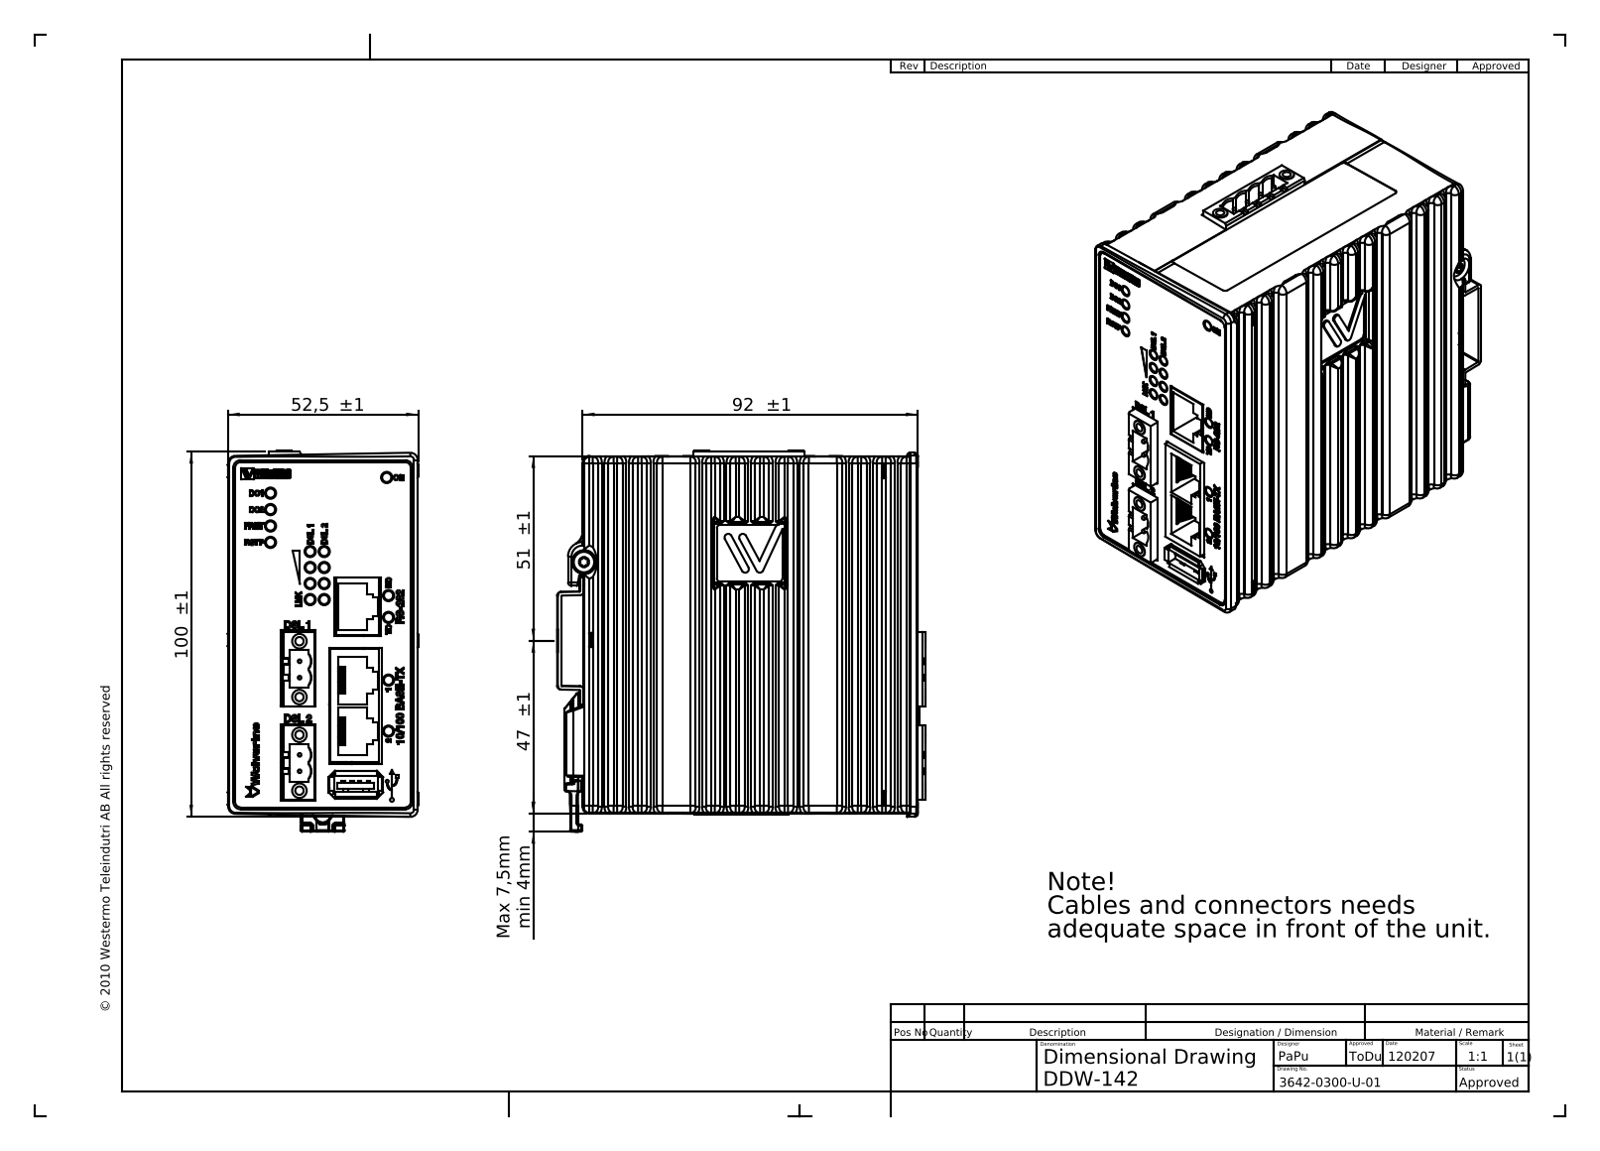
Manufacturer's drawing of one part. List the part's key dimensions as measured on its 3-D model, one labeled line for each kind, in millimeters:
Part name (STEP PRODUCT): 3642-0300; Pan Head Cross Recess Screw_ISO_ISO 7045 - M3 x 6 - Z --- 6N; MRT-TT-M2.5x6H-steel-fzb-Bufab_MRT-TT-M2.5x6H-steel-fzb-Bufab; 9003-0134_assy.encl.DIN_Lock_Lynx_cc (+8 more)
STEP written by: SolidWorks 2011 (CONFIG_CONTROL_DESIGN)
Units: millimetres
Bodies: 23 solids, 6868 faces (2562 planar, 1579 cylindrical, 2727 other)
Overall size (bounding box): 104.48 × 101.2 × 52.3
Volume: 145 887 mm³ · Surface area: 160 956 mm²
Round holes (diameter × count): ⌀2.5 ×23, ⌀3.1 ×17, ⌀0.9 ×16, ⌀2.3 ×6, ⌀3.2 ×6, ⌀1.2 ×4, ⌀1.25 ×4, ⌀1.3 ×4, ⌀3.57 ×4, ⌀1.52 ×2, ⌀1.73 ×2, ⌀2.3 ×2
Round bosses / shafts (diameter × count): ⌀1 ×18, ⌀4 ×7, ⌀1.6 ×5, ⌀1.2 ×4, ⌀5.6 ×3, ⌀3.5 ×2, ⌀3.3 ×2, ⌀5 ×1
Partial cylindrical surfaces — rounded edges, fillets, slot ends (radius × count): R0.3 ×138, R0.4 ×129, R0.2 ×104, R0.5 ×87, R1 ×87, R1.5 ×64, R0.1 ×21, R0.9 ×18
Main face-to-face distances: 1.6, 31.9, 14.3, 17.6, 30.3, 12.7, 15.9, 19.2, 33.5, 16
Hole centre spacings: 2, 2.83, 4, 4.47, 6, 6.32, 8, 8.25
